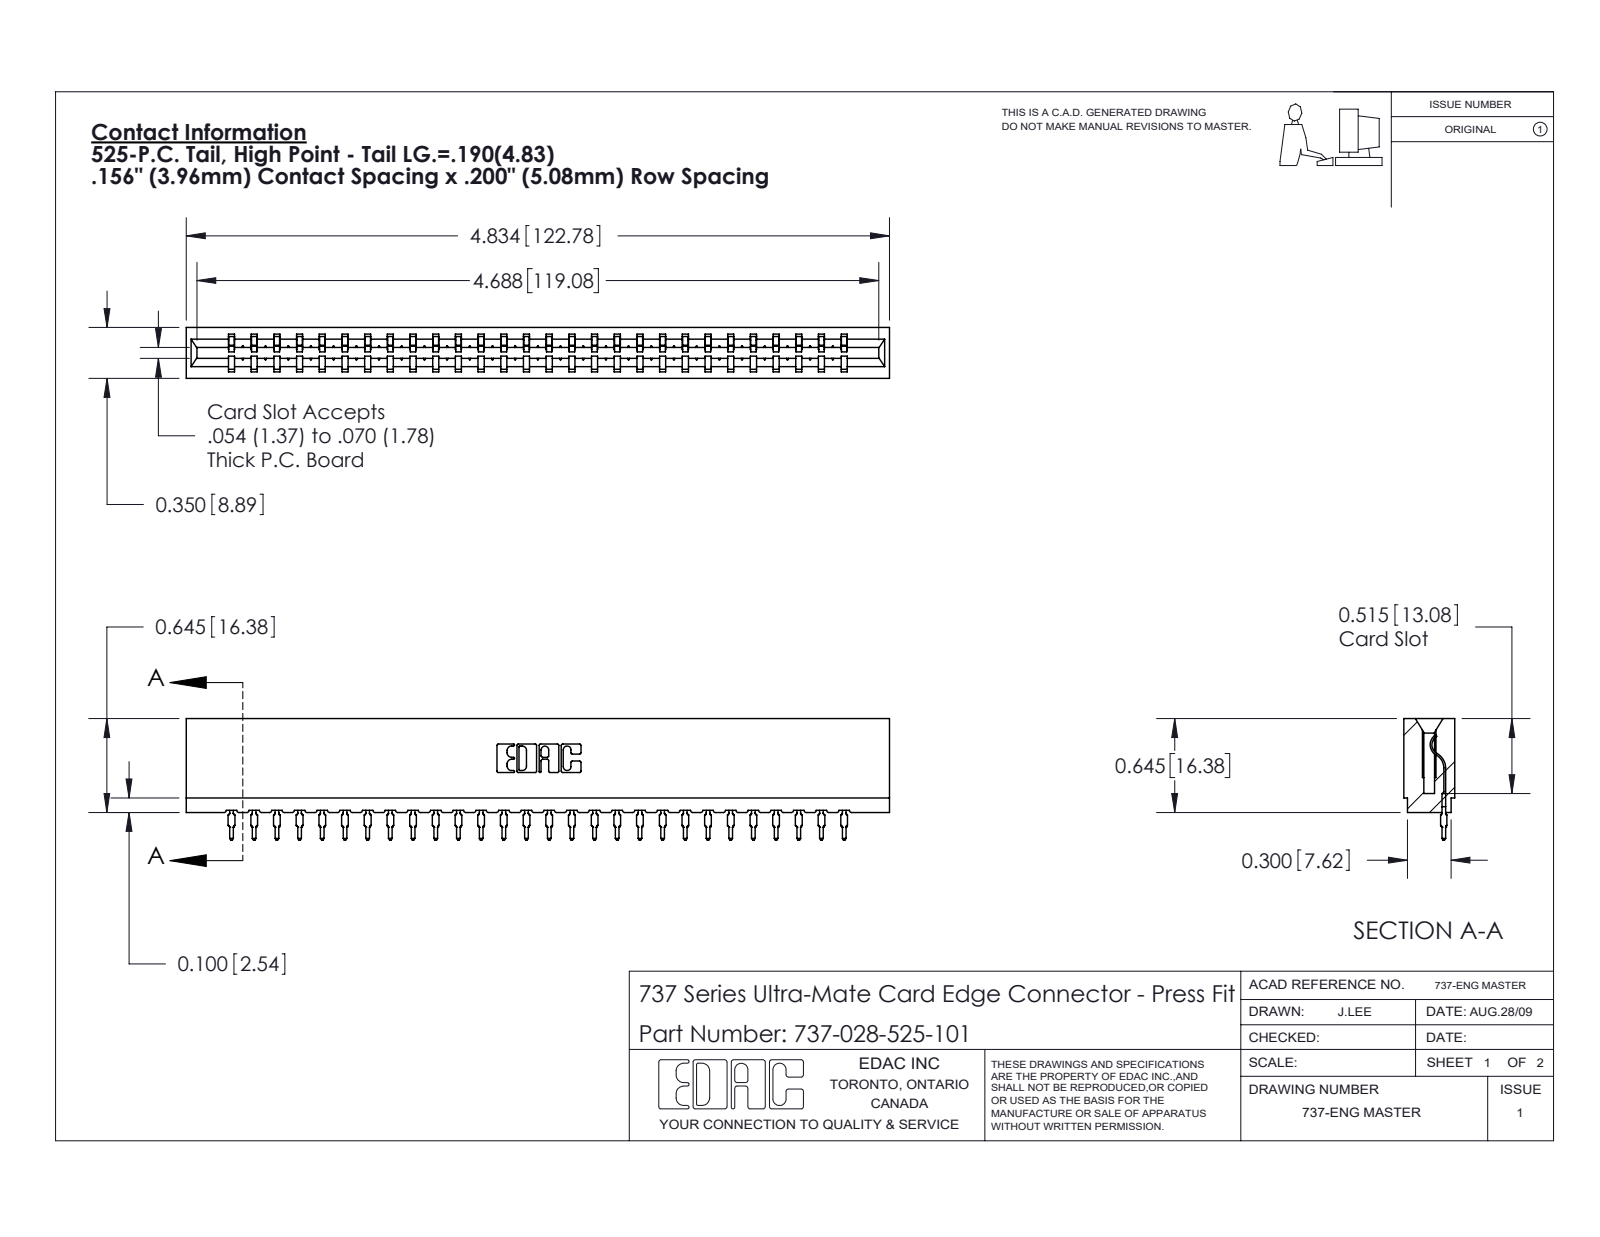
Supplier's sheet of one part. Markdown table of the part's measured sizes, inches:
| quantity | value |
| --- | --- |
| part name | 745-292-001_525; 737-028-525-101; 737 Part_Insulator Option - 01 |
| STEP written by | SolidWorks 2020 (CONFIG_CONTROL_DESIGN) |
| units | inches |
| bodies | 29 solids, 3258 faces (1958 planar, 572 cylindrical, 728 other) |
| overall size | 4.834 × 0.836 × 0.35 |
| volume | 0.729 in³ |
| surface area | 24.35 in² |
| partial cylindrical surfaces (radius × count) | 0.015 × 56, 0.021 × 56, 0.01 × 22, 0.007 × 6, 0.031 × 6, 0.005 × 4, 0.011 × 4, 0.026 × 3 |
| main face-to-face distances | 0.138, 0.212, 0.35, 0.074, 0.624, 0.045, 0.305, 0.093, 0.167, 0.156 |
